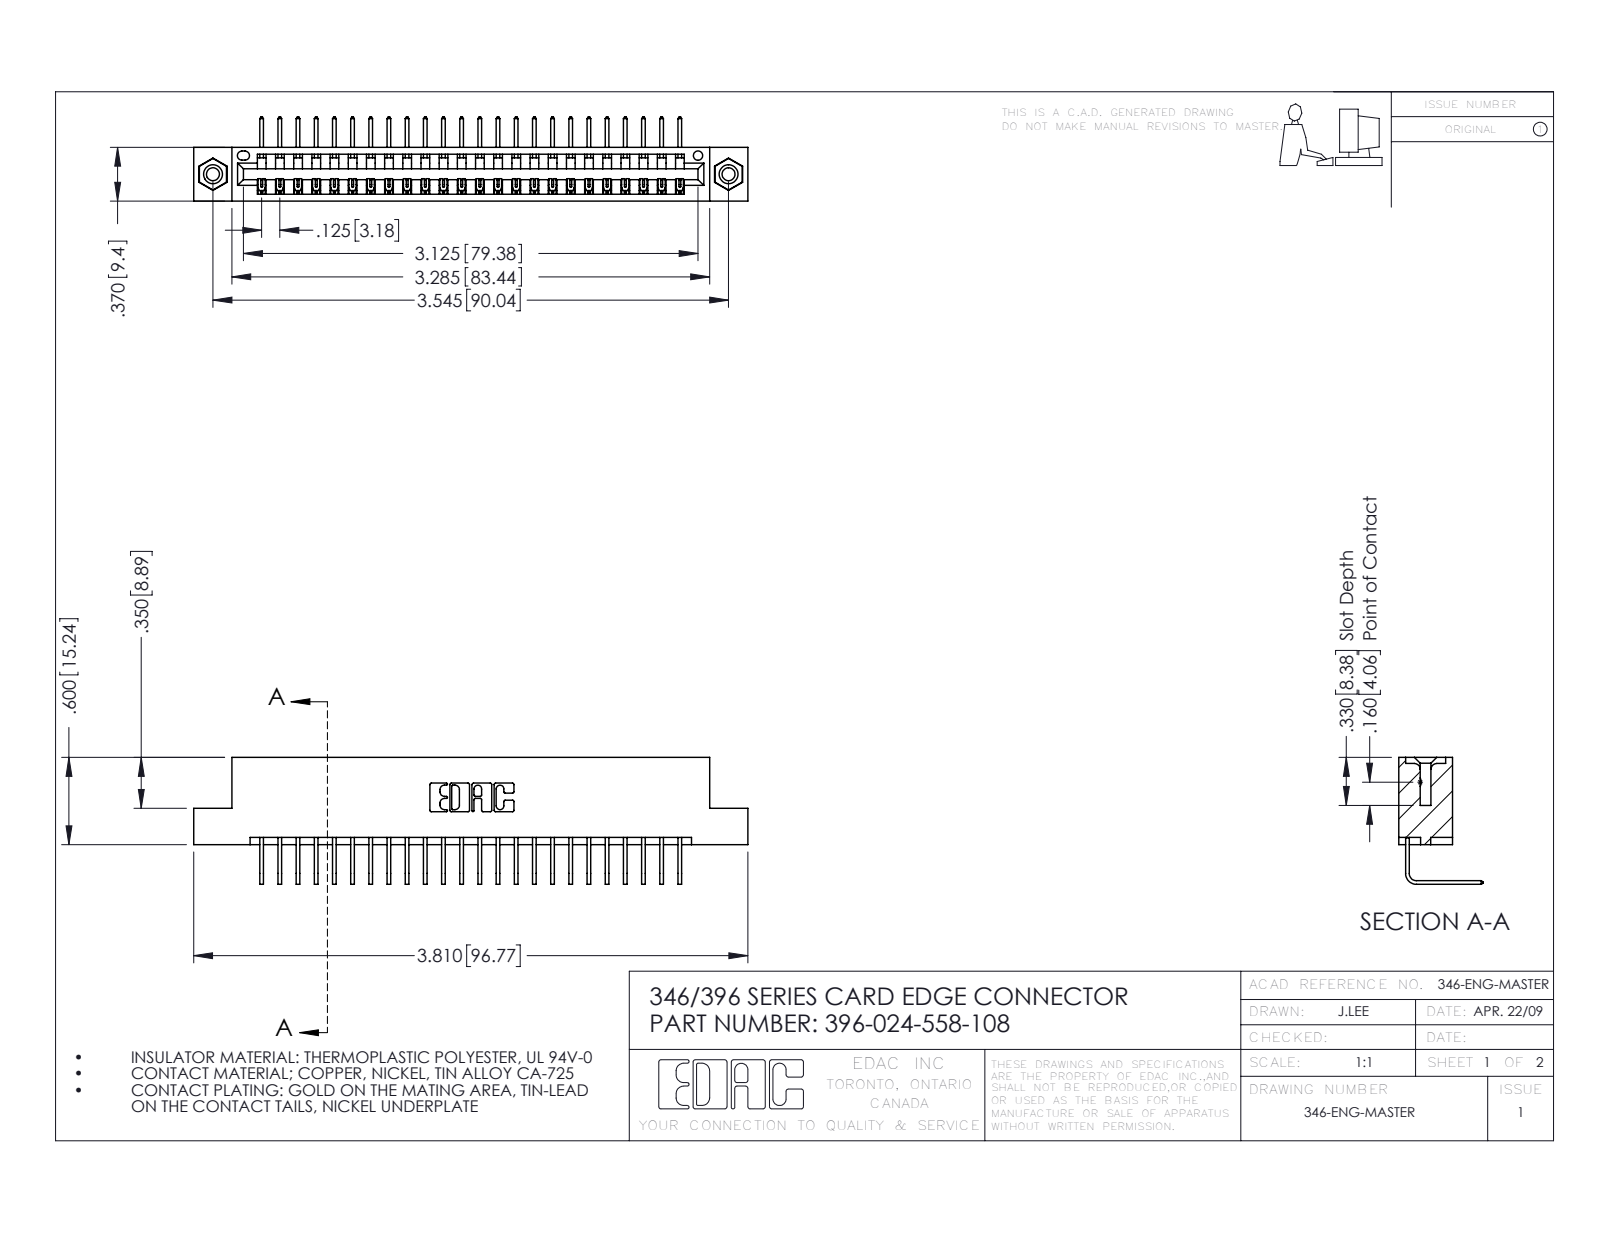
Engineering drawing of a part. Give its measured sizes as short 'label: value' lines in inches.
name: 346 Part_Flush Mounting Lugs - 0.156 Dia-TI; 345-292-001_558 Tail - 2; 345-250-001_345-250-003-102; 396-024-558-108
written by: SolidWorks 2016 (CONFIG_CONTROL_DESIGN)
unit: in
bodies: 27 solids, 1622 faces (1116 planar, 490 cylindrical, 16 other)
size: 3.81 × 0.873 × 0.58
volume: 0.562 in³; area: 18.32 in²
holes: 2× ⌀0.089, 2× ⌀0.125, 2× ⌀0.156, 1× ⌀0.064
bosses: 2× ⌀0.155
rounds: 48× R0.006, 22× R0.01, 6× R0.007, 6× R0.031, 3× R0.026, 2× R0.031, 2× R0.04, 1× R0.014
face distances: 0.322, 0.048, 0.37, 0.25, 0.298, 0.025, 0.072, 0.148, 0.222, 0.1
hole spacings: 0.246, 3.337, 3.545
